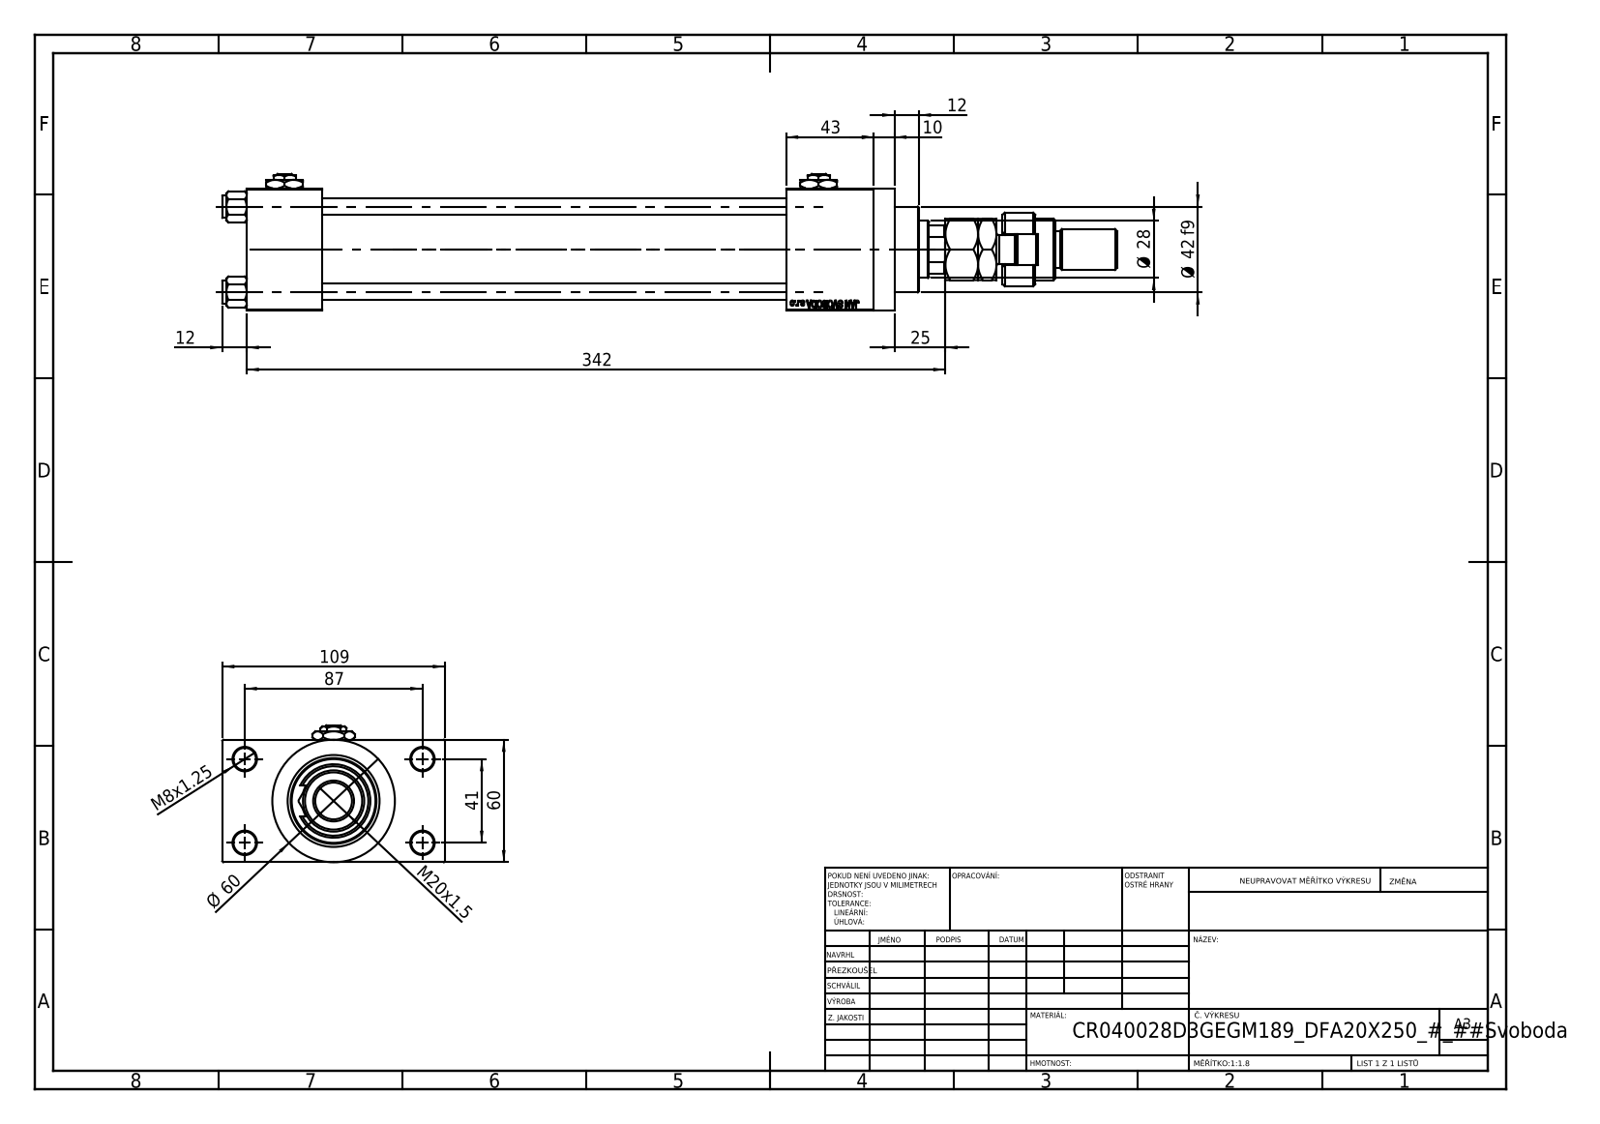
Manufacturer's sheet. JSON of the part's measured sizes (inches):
{"part_name": "NUT_M5_D; FEMALE_PART_FOR_DFA; MFA; Zatka_pro_OIL_PORT (+4 more)", "step_written_by": "SolidWorks 2019 (CONFIG_CONTROL_DESIGN)", "units": "inches", "bodies": {"solids": 15, "faces": 1291, "planar": 574, "cylindrical": 113, "other": 604}, "overall_size": [17.244, 4.291, 2.638], "volume_in3": 48.05, "surface_area_in2": 342.9, "round_holes": [[0.315, 4], [0.433, 4], [0.276, 2], [0.656, 2], [0.945, 2], [0.728, 1], [1.102, 1], [1.22, 1], [1.575, 1], [1.772, 1]], "round_bosses_or_shafts": [[0.433, 4], [2.362, 1], [1.811, 1], [1.654, 1], [1.417, 1], [1.181, 1], [0.866, 1], [0.787, 1]], "partial_cylinders_radius": [[0.295, 1], [0.472, 1], [0.531, 1]], "face_to_face_distances": [2.362, 0.965, 3.327, 8.937, 1.457, 10.394, 1.693, 12.087, 10.63, 4.291], "hole_center_spacings": [0.892, 1.161, 1.642, 1.856, 1.893, 2.533, 3.011, 1.614]}
